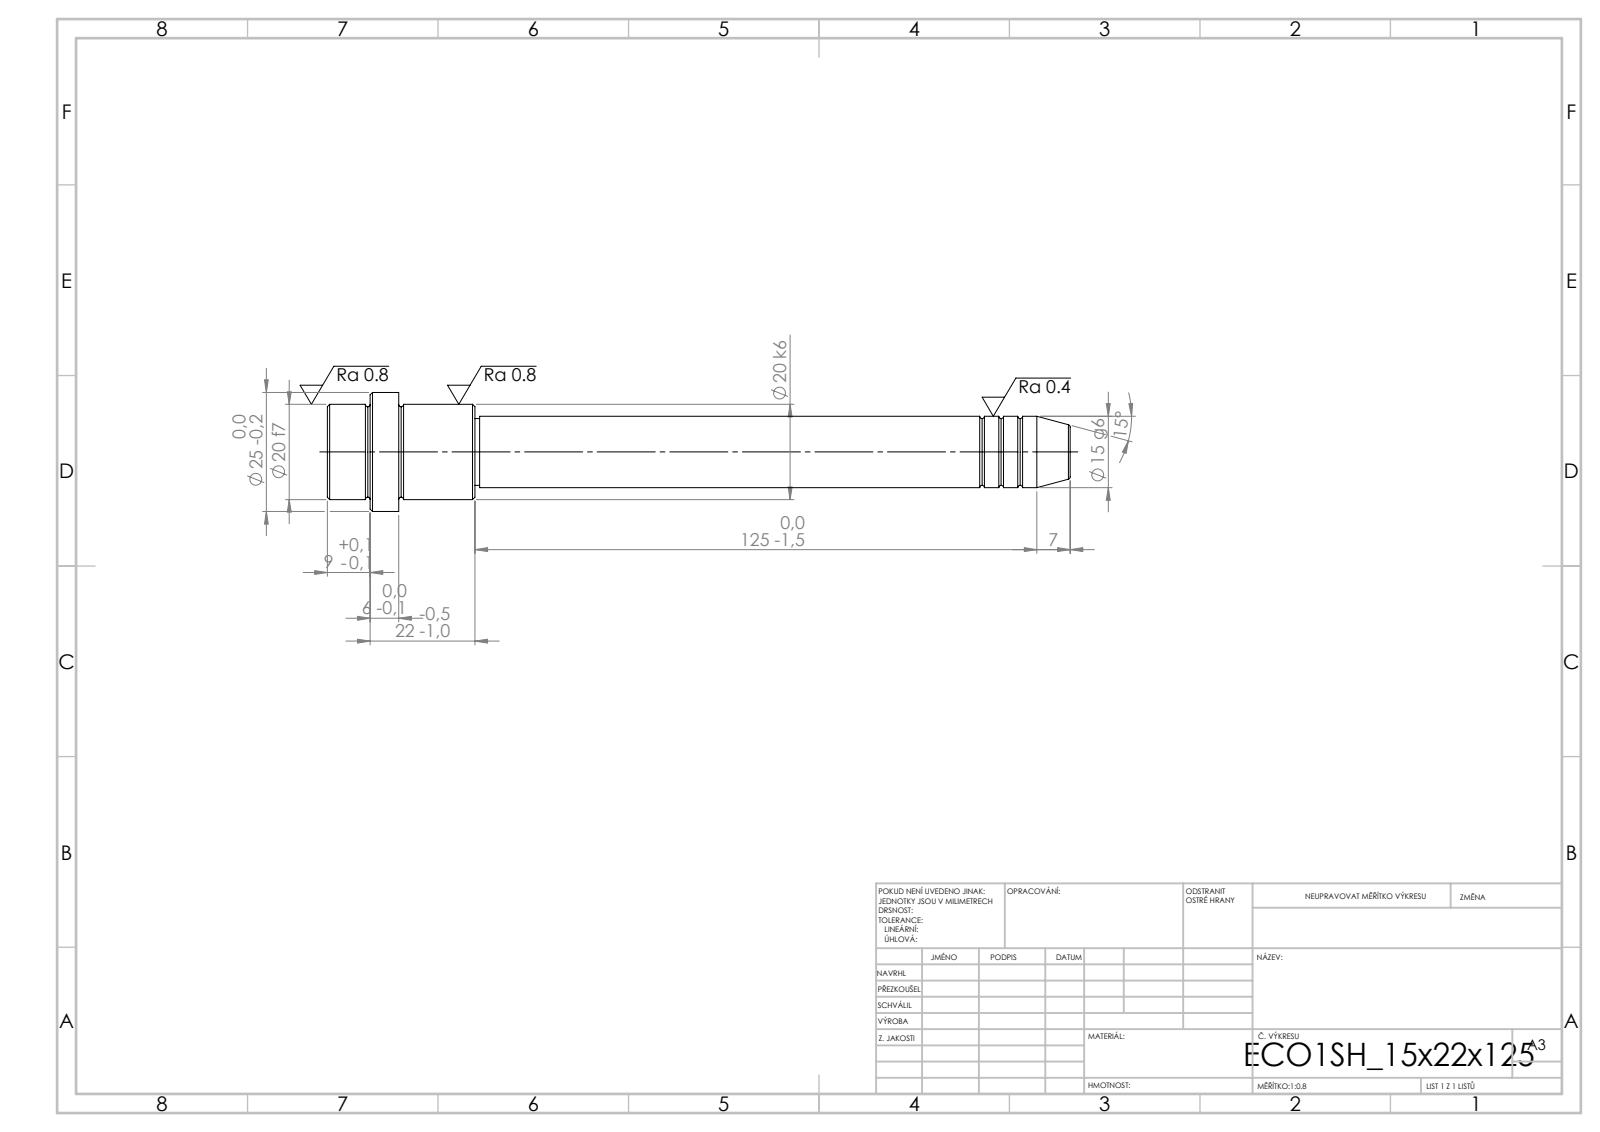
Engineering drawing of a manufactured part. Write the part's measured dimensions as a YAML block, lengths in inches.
step_written_by: "SolidWorks 2019 (CONFIG_CONTROL_DESIGN)"
units: inches
bodies: {solids: 1, faces: 52, planar: 6, cylindrical: 16, other: 30}
overall_size: [6.142, 0.984, 0.984]
volume: 1.98
surface_area: 13.83
round_bosses_or_shafts:
  - {diameter: 0.984, count: 1}
  - {diameter: 0.787, count: 1}
  - {diameter: 0.591, count: 1}
  - {diameter: 0.551, count: 1}
face_to_face_distances: [0.591, 0.236, 0.354, 0.63, 0.866, 1.22, 4.921, 5.551, 5.787, 6.142]
